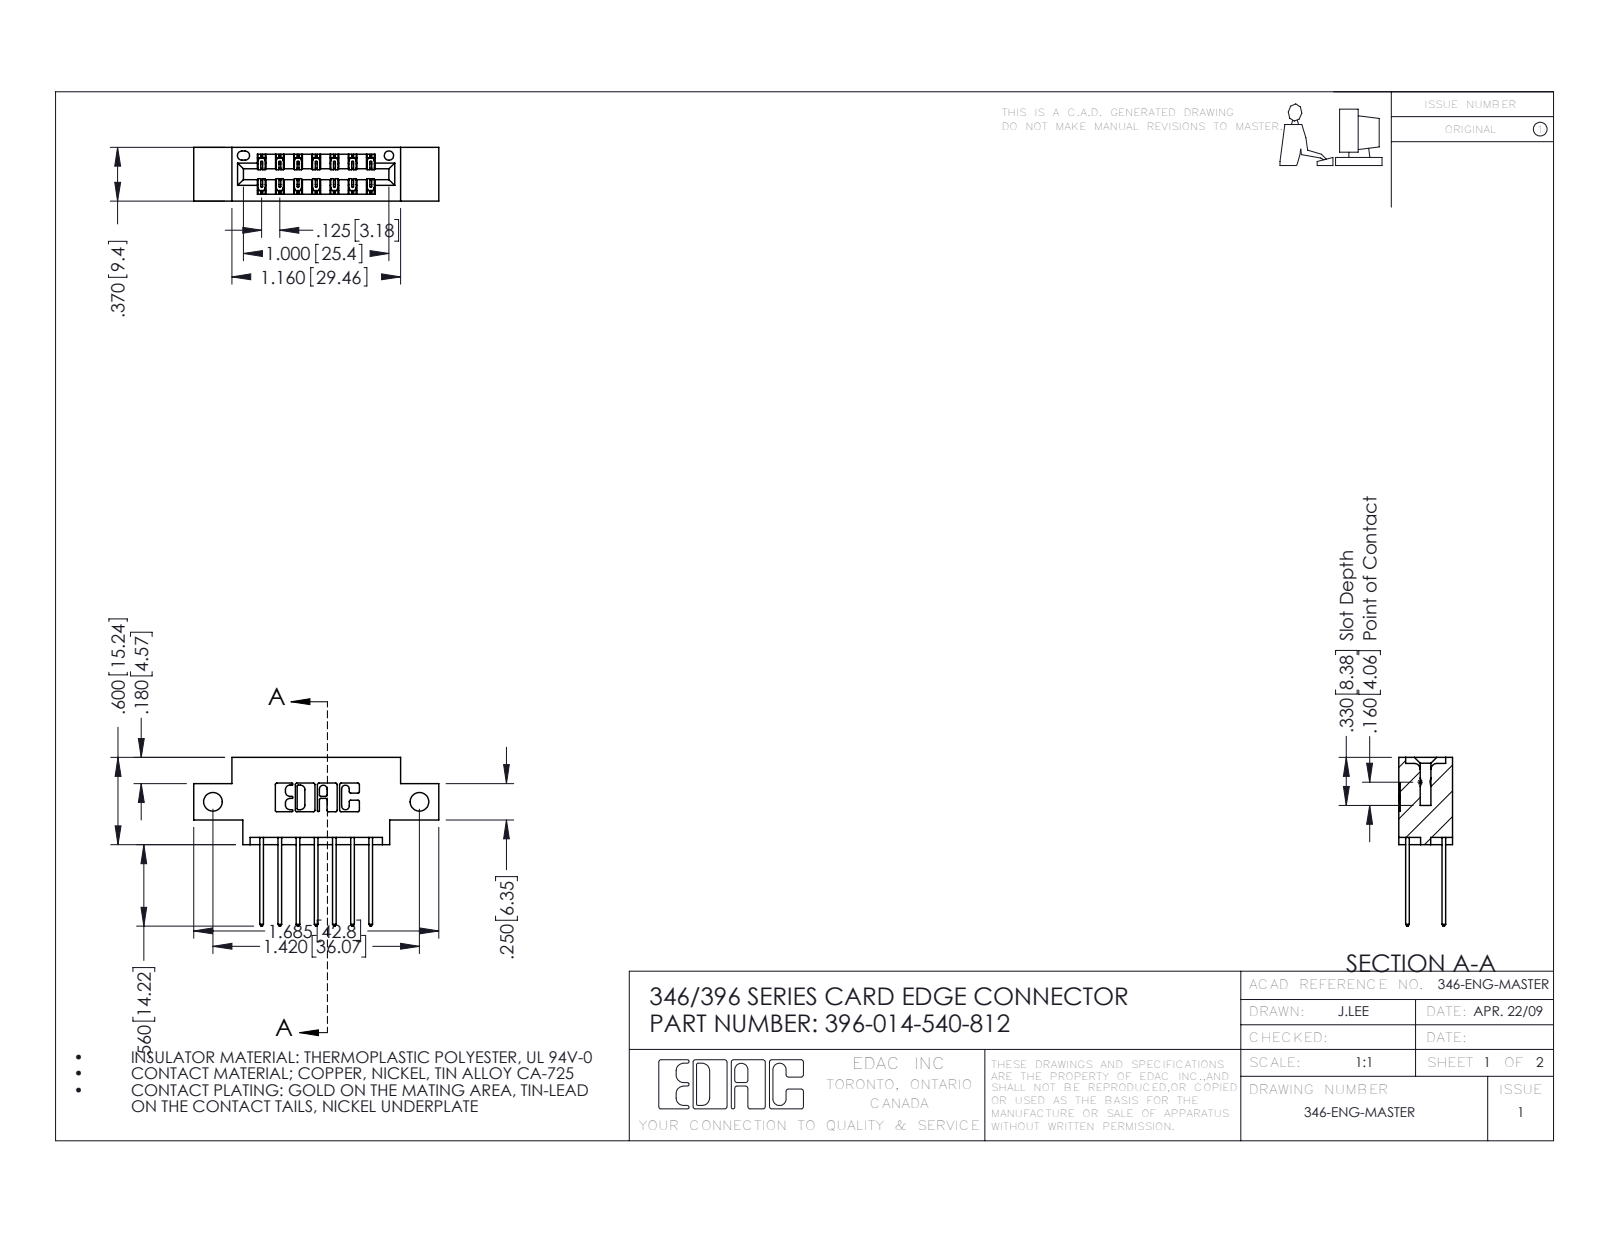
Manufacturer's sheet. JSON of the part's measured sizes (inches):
{"part_name": "396-014-540-812; 346 Part_0.170 Offset - Side Mount; 345-292-001_345-293-140", "step_written_by": "SolidWorks 2016 (CONFIG_CONTROL_DESIGN)", "units": "inches", "bodies": {"solids": 15, "faces": 854, "planar": 570, "cylindrical": 284, "other": 0}, "overall_size": [1.685, 1.16, 0.37], "volume_in3": 0.227, "surface_area_in2": 7.512, "round_holes": [[0.128, 2], [0.064, 1]], "partial_cylinders_radius": [[0.01, 22], [0.006, 21], [0.01, 14], [0.007, 6], [0.031, 6], [0.026, 3], [0.014, 2], [0.022, 2]], "face_to_face_distances": [0.25, 0.048, 0.322, 0.37, 0.072, 0.298, 0.025, 0.275, 0.225, 0.148], "hole_center_spacings": [1.42]}
